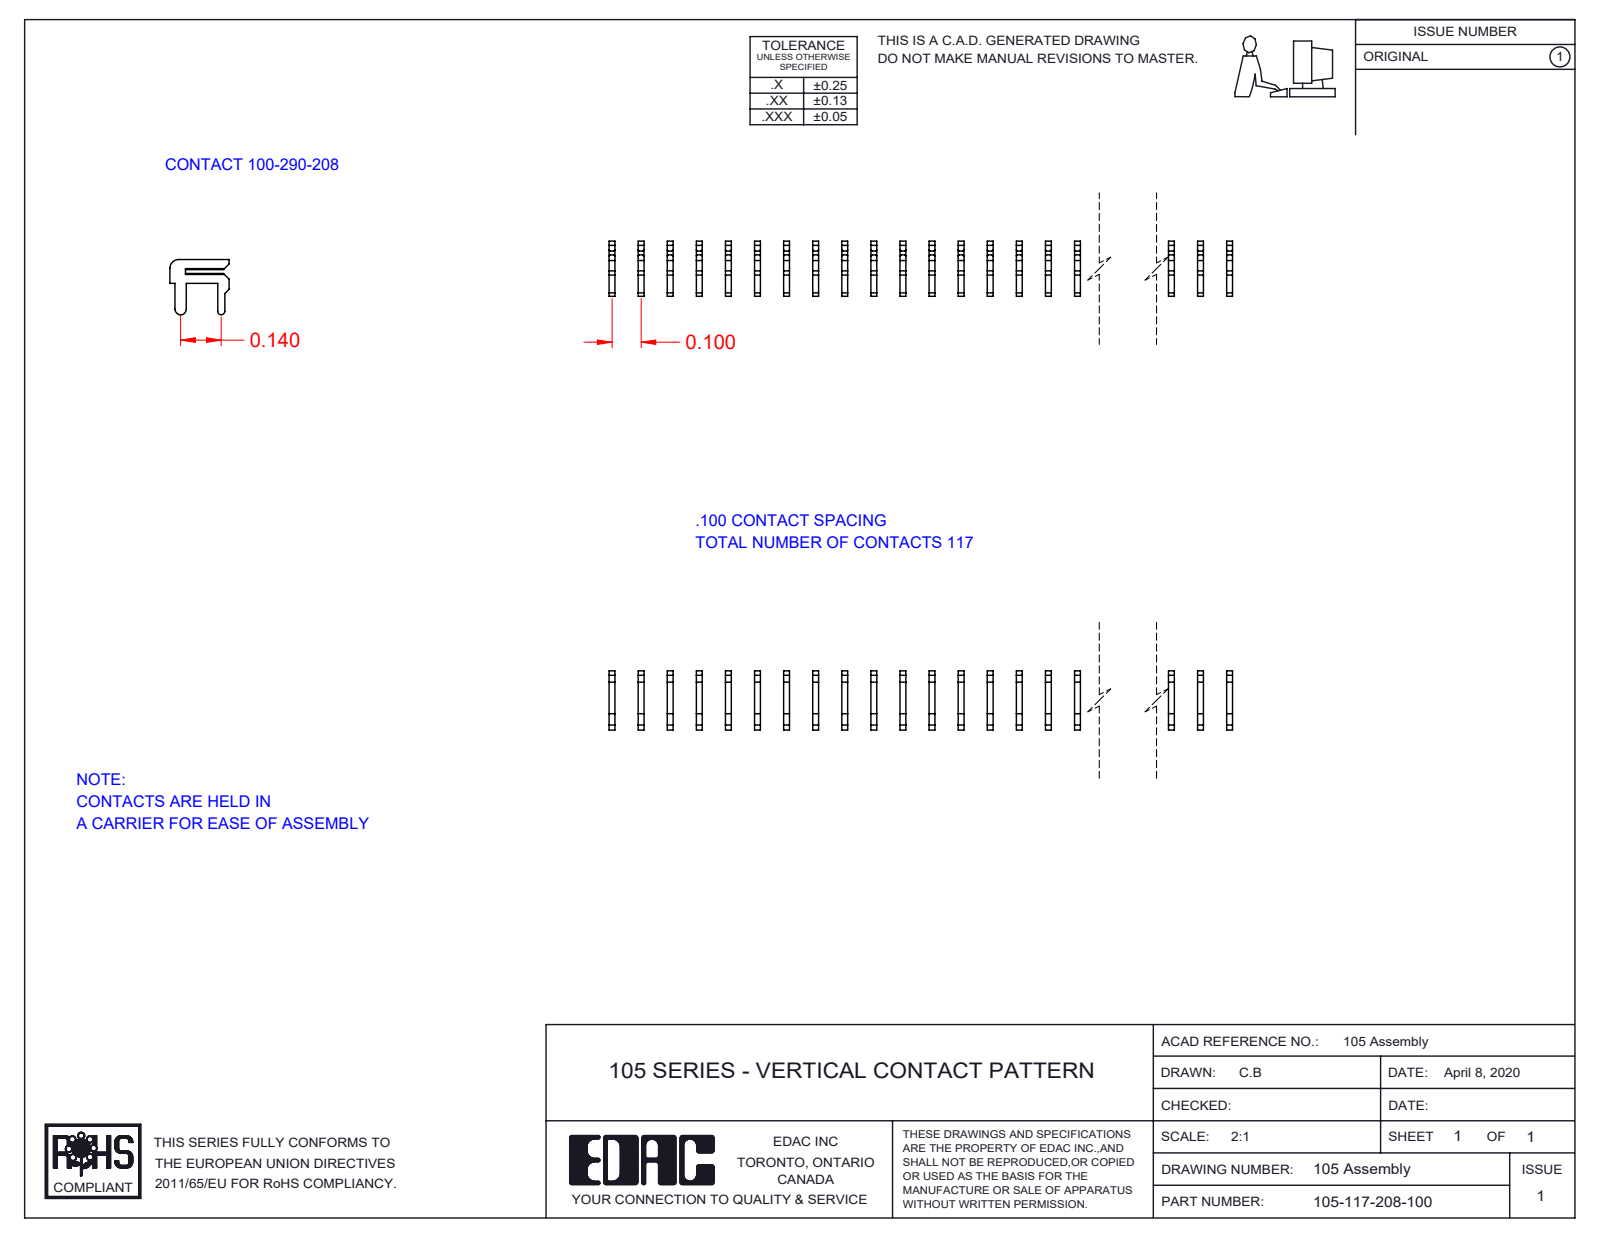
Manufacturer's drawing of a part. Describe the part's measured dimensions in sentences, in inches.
The part is named "100-290-001_100-290-208; 105-117-208-100". Its 3-D file was written by "SolidWorks 2016 (CONFIG_CONTROL_DESIGN)". It is 117 solids with 2925 faces: 2574 planar, 351 cylindrical and 0 other. Overall it measures 11.62 by 0.204 by 0.19 inches. Its volume is 0.049 cubic inches and its surface area 7.707 square inches. Partial cylindrical surfaces (rounded edges, fillets, slot ends): 1 of radius 0.012, 1 of radius 0.019, 1 of radius 0.03. The main face-to-face distances are 0.034, 0.048, 0.1, 0.2, 0.3, 0.039, 0.147, 0.4, 0.5, 0.082.
